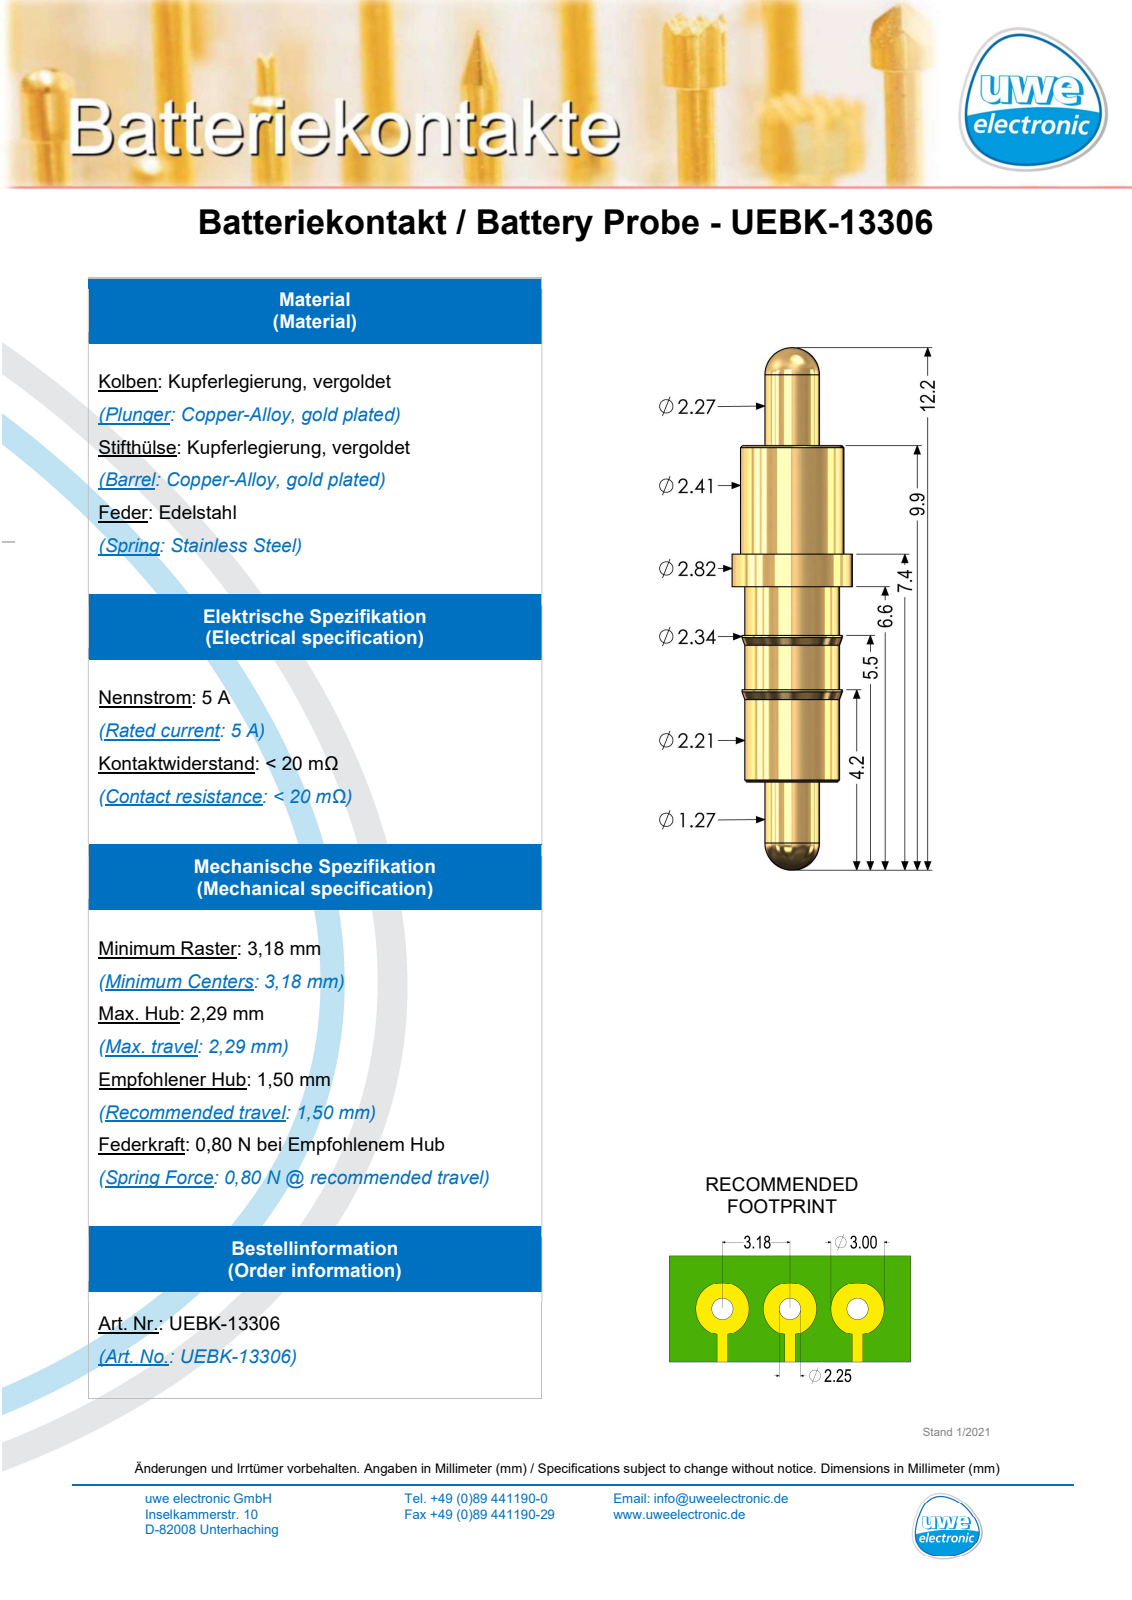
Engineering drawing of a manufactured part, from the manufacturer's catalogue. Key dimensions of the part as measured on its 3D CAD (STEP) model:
Part name (STEP PRODUCT): UEBK-13306
STEP written by: SolidWorks 2019 (AUTOMOTIVE_DESIGN)
Units: millimetres
Bodies: 1 solid, 36 faces (6 planar, 18 cylindrical, 12 other)
Overall size (bounding box): 12.22 × 2.8 × 2.8
Volume: 39 mm³ · Surface area: 86 mm²
Round bosses / shafts (diameter × count): ⌀2.8 ×1, ⌀2.41 ×1, ⌀2.34 ×1, ⌀2.21 ×1, ⌀1.27 ×1
Main face-to-face distances: 3.3, 4.57, 7.87, 5.33, 0.76, 2.54, 3.43, 1.14, 1.9, 4.44
